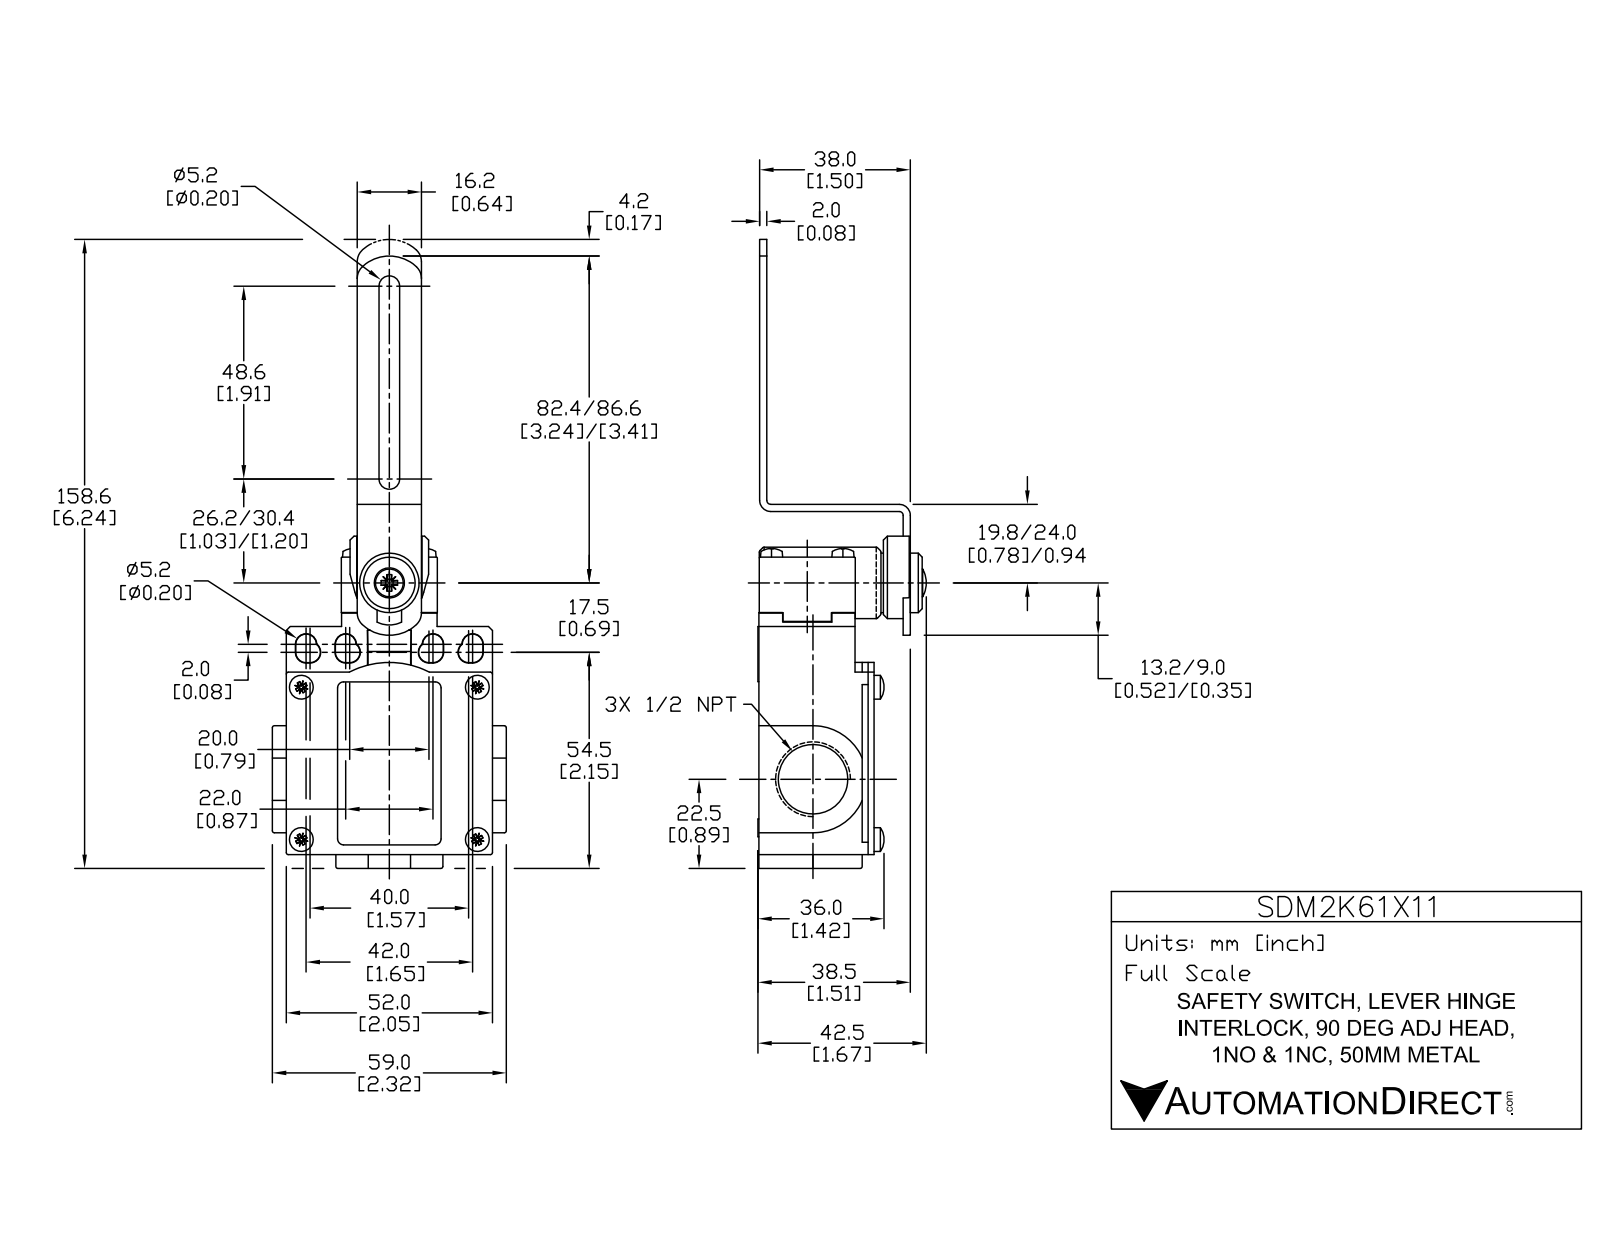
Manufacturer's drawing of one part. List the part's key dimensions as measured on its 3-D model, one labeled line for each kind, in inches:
Part name (STEP PRODUCT): SDM2K61X11
STEP written by: SolidWorks 2017 (AUTOMOTIVE_DESIGN)
Units: inches
Bodies: 5 solids, 293 faces (152 planar, 107 cylindrical, 34 other)
Overall size (bounding box): 6.161 × 2.323 × 1.656
Volume: 6.167 in³ · Surface area: 39.86 in²
Round holes (diameter × count): ⌀0.669 ×2, ⌀0.748 ×2, ⌀0.299 ×1, ⌀0.433 ×1
Round bosses / shafts (diameter × count): ⌀0.22 ×4, ⌀0.217 ×4, ⌀0.709 ×1, ⌀0.591 ×1, ⌀0.276 ×1
Partial cylindrical surfaces — rounded edges, fillets, slot ends (radius × count): R0.02 ×14, R0.102 ×14, R0.157 ×4, R0.394 ×3, R0.039 ×2, R0.11 ×2, R0.283 ×2, R0.531 ×2
Main face-to-face distances: 1.144, 0.071, 1.496, 0.138, 1.425, 2.047, 0.945, 0.551, 0.689, 2.307
